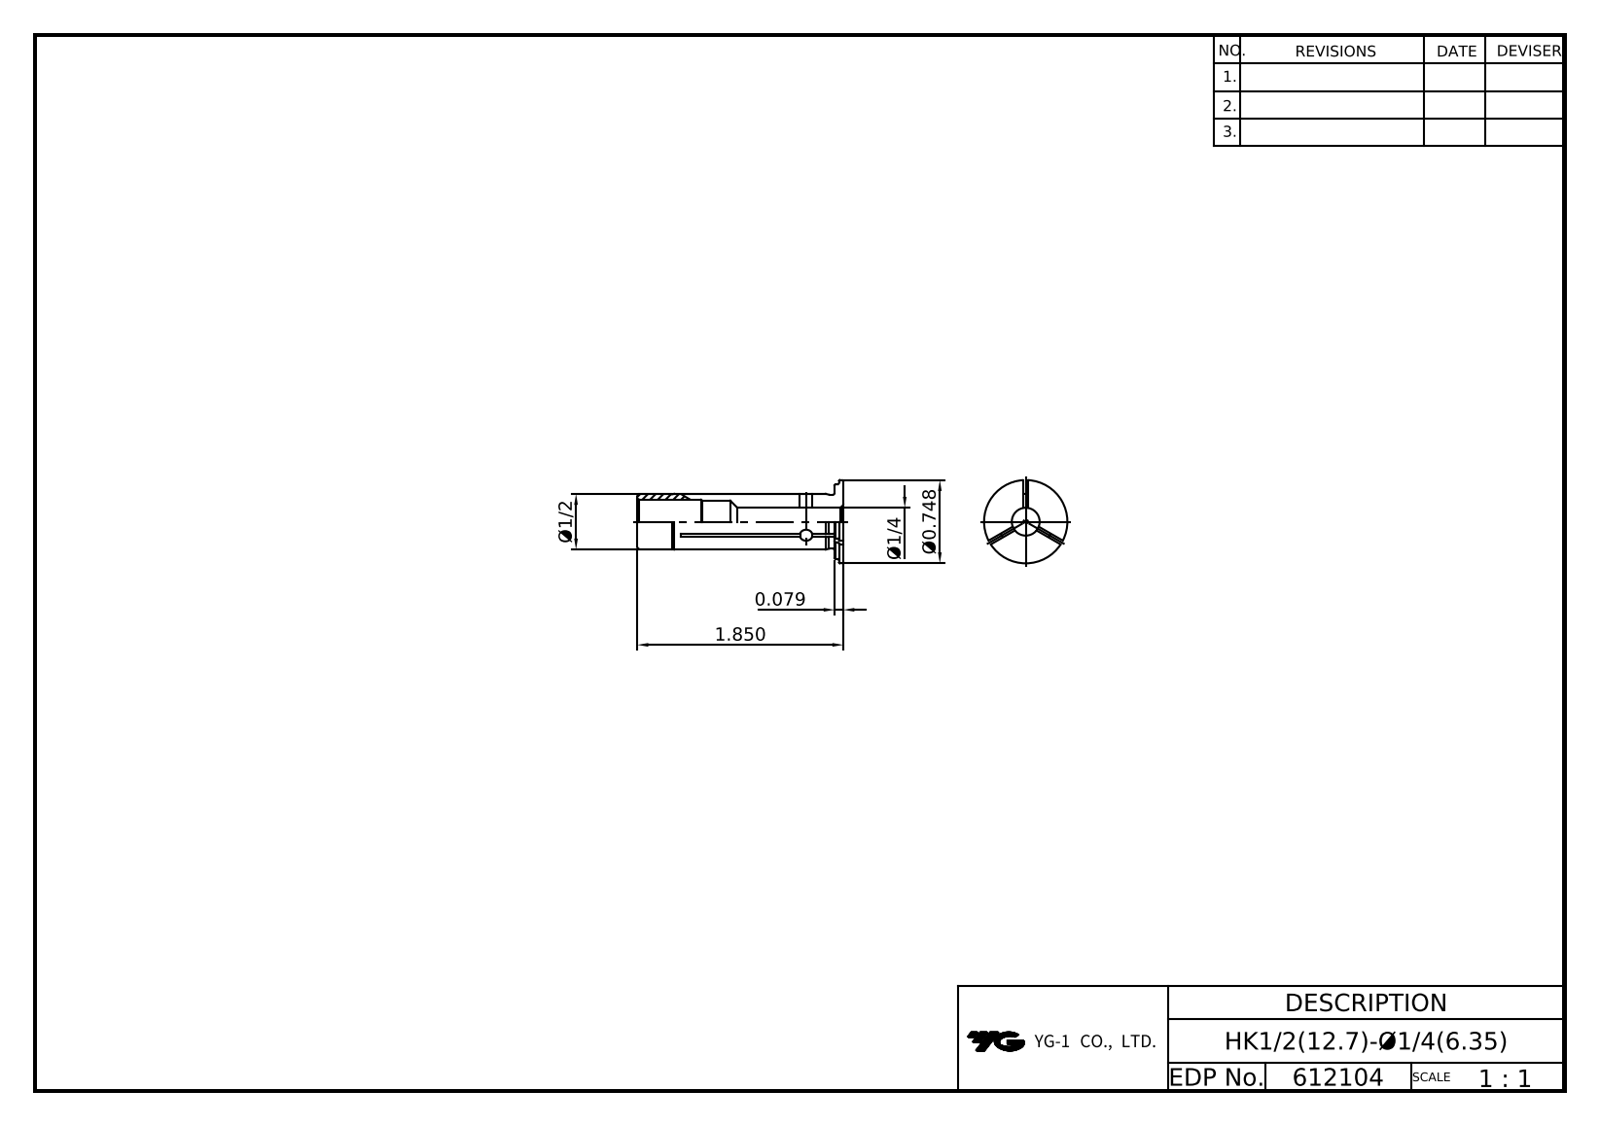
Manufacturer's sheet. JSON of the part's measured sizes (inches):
{"part_name": "HK12_7-6_35", "step_written_by": "PRO/ENGINEER BY PARAMETRIC TECHNOLOGY CORPORATION, 2012130 (CONFIG_CONTROL_DESIGN)", "units": "inches", "bodies": {"solids": 1, "faces": 97, "planar": 25, "cylindrical": 36, "other": 36}, "overall_size": [1.85, 0.748, 0.748], "volume_in3": 0.204, "surface_area_in2": 6.017, "round_holes": [[0.114, 3], [0.25, 1], [0.378, 1], [0.394, 1]], "round_bosses_or_shafts": [[0.748, 1], [0.669, 1], [0.5, 1], [0.492, 1], [0.484, 1]], "partial_cylinders_radius": [[1.476, 3]], "face_to_face_distances": [0.039, 0.079, 1.772, 1.811, 1.85]}
